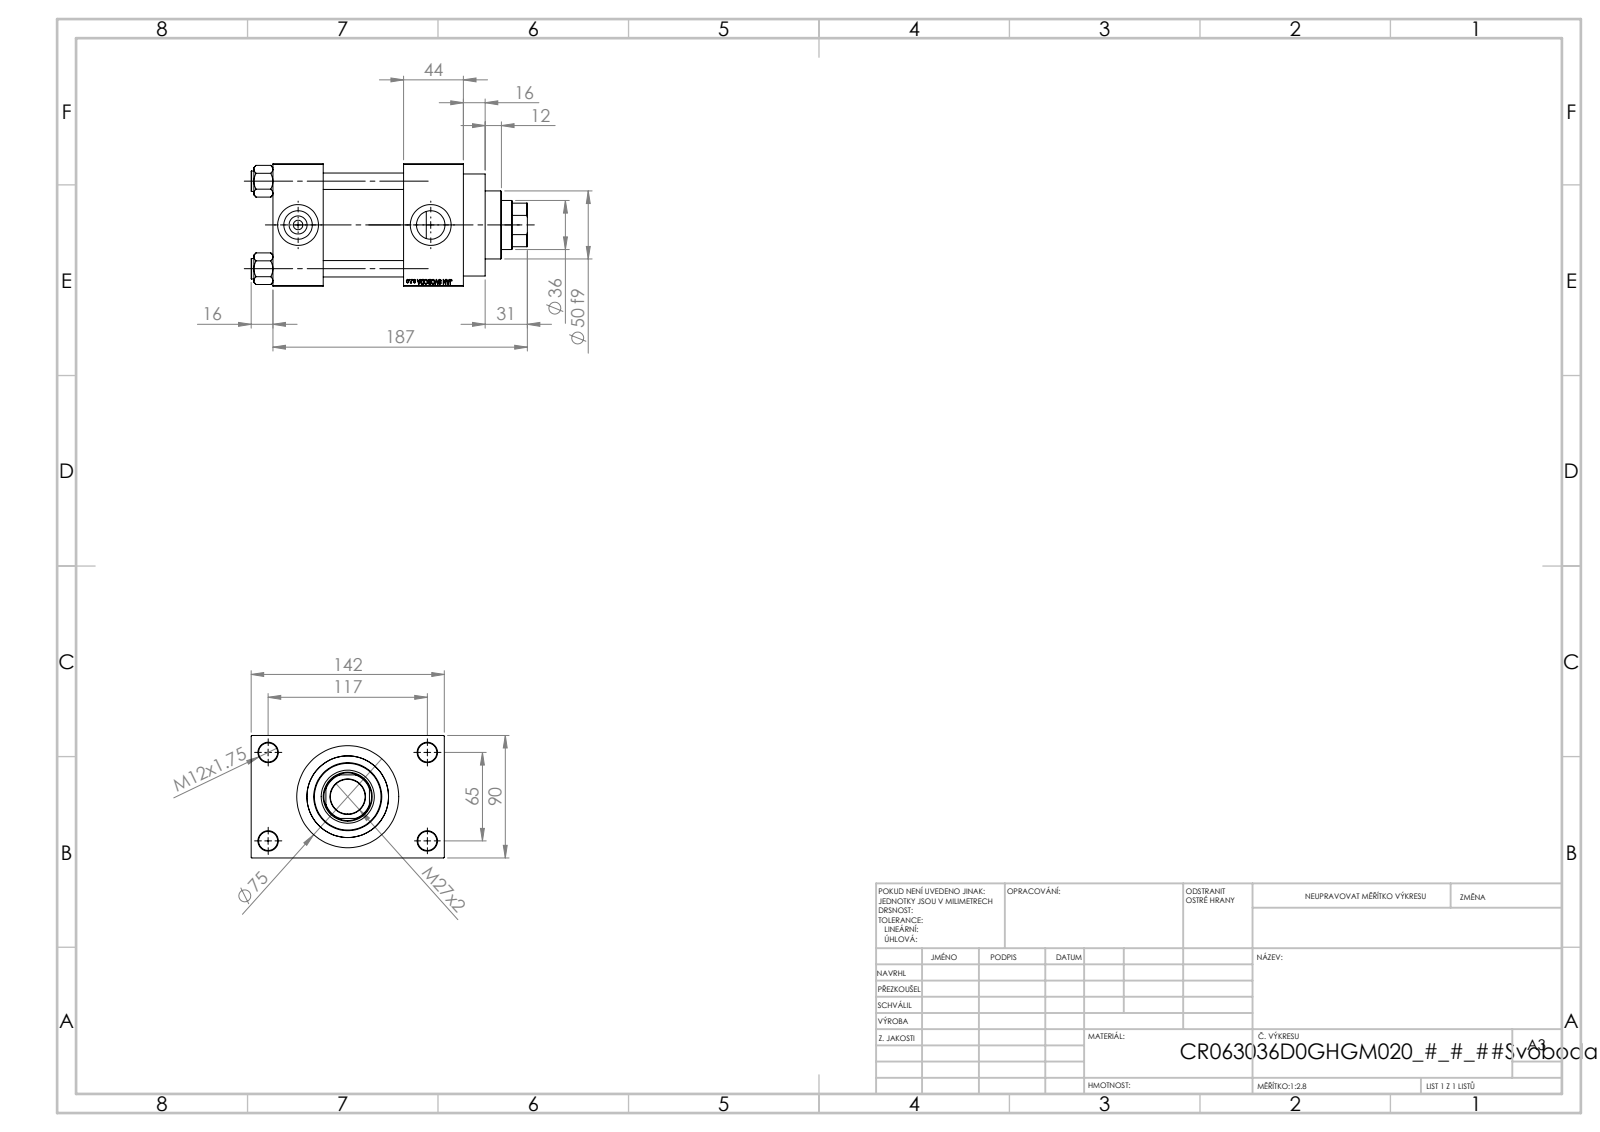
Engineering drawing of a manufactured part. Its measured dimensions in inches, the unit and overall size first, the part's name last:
Units: inches
Overall size (bounding box): 7.992 × 5.591 × 3.543
Round holes (diameter × count): ⌀0.472 ×4, ⌀0.551 ×4, ⌀0.276 ×2, ⌀0.825 ×2, ⌀1.181 ×2, ⌀1.004 ×1, ⌀1.417 ×1, ⌀1.535 ×1, ⌀1.969 ×1, ⌀2.362 ×1, ⌀2.48 ×1
Round bosses / shafts (diameter × count): ⌀0.591 ×4, ⌀2.953 ×1, ⌀2.717 ×1
Partial cylindrical surfaces — rounded edges, fillets, slot ends (radius × count): R0.689 ×1
Main face-to-face distances: 3.543, 2.323, 1.457, 3.78, 5.512, 4.055, 1.732, 1.024, 4.567, 5.591
Hole centre spacings: 1.037, 1.79, 2.531, 2.635, 2.748, 3.569, 4.383, 2.559
Volume: 67.86 in³ · Surface area: 319 in²
Bodies: 11 solids, 1103 faces (497 planar, 88 cylindrical, 518 other)
Part name (STEP PRODUCT): V215CR_VCP_D; V215_VC_A; NUT_M5_D; V215CR_D_TYCINKA (+1 more)
STEP written by: SolidWorks 2019 (CONFIG_CONTROL_DESIGN)
